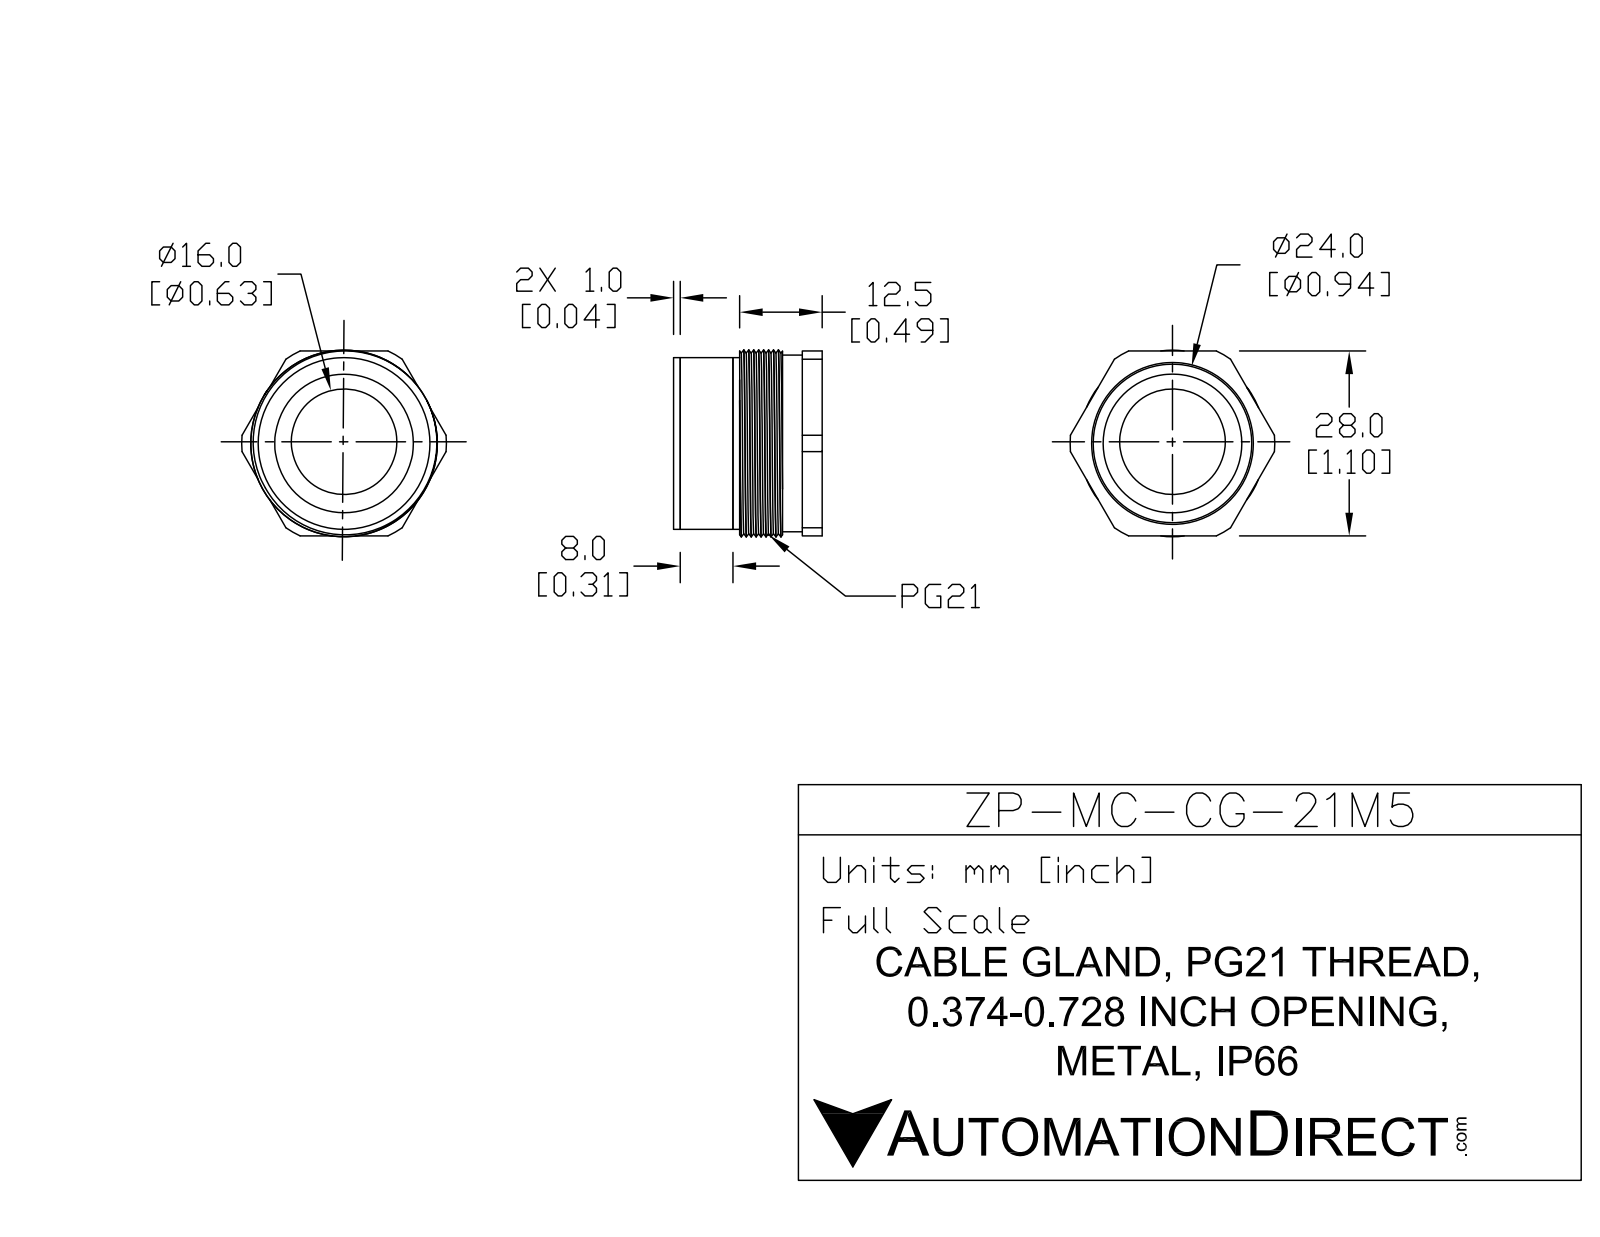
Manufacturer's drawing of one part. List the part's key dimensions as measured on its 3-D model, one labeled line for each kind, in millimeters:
Part name (STEP PRODUCT): ZP-MC-CG-21M5
STEP written by: SolidWorks 2011 (AUTOMOTIVE_DESIGN)
Units: millimetres
Bodies: 3 solids, 35 faces (16 planar, 15 cylindrical, 4 other)
Overall size (bounding box): 31 × 28.25 × 22.5
Volume: 5 108 mm³ · Surface area: 5 531 mm²
Round holes (diameter × count): ⌀16 ×1, ⌀21 ×1, ⌀24 ×1
Round bosses / shafts (diameter × count): ⌀28.25 ×1, ⌀26.75 ×1, ⌀26 ×1
Partial cylindrical surfaces — rounded edges, fillets, slot ends (radius × count): R15.5 ×1
Main face-to-face distances: 8, 1, 9, 13.5, 21.5, 12.5, 22.5, 10, 3, 28
